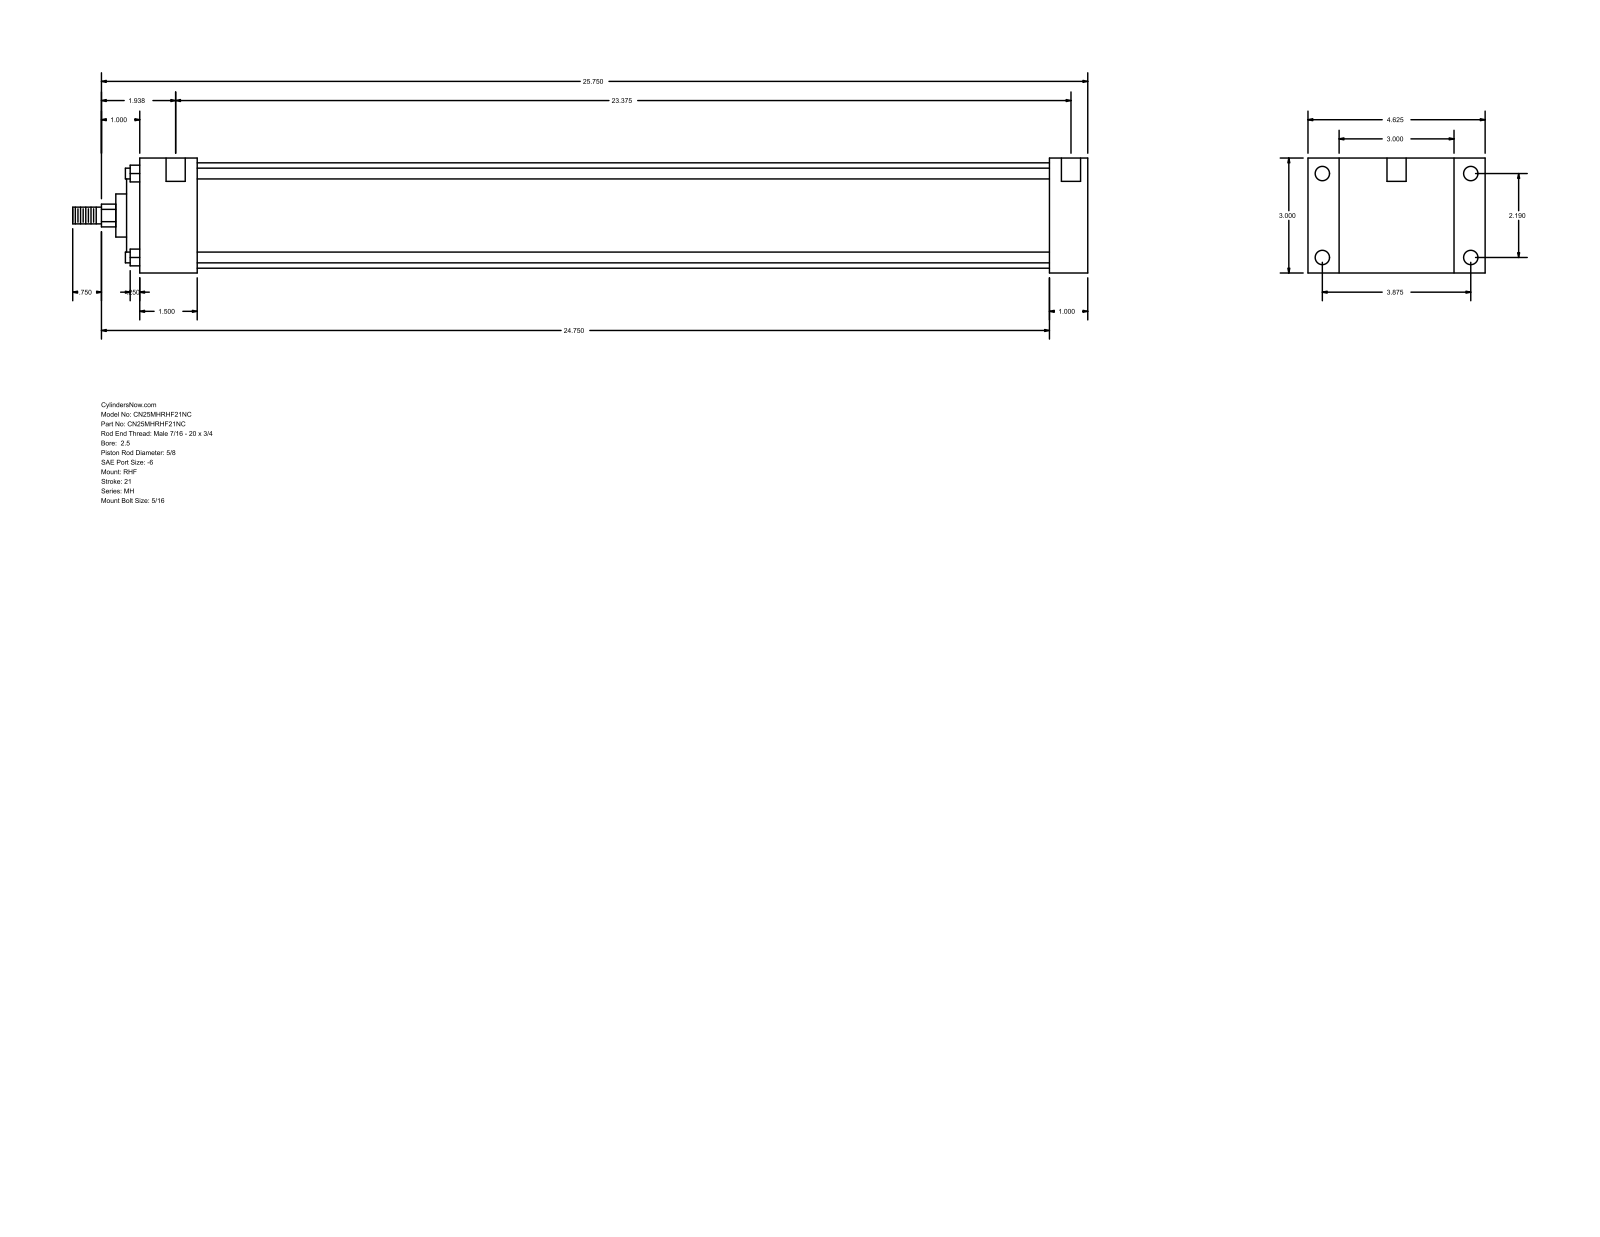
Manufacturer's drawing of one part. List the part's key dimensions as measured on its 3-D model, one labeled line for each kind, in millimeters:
Part name (STEP PRODUCT): MH_RHF__0250_0.625
STEP written by: GSSL Pune (CONFIG_CONTROL_DESIGN)
Units: millimetres
Bodies: 0 solids, 90 faces (61 planar, 29 cylindrical, 0 other)
Overall size (bounding box): 673.1 × 117.47 × 76.2
Round holes (diameter × count): ⌀5.56 ×4, ⌀9.53 ×4, ⌀12.7 ×2
Round bosses / shafts (diameter × count): ⌀7.14 ×4, ⌀69.85 ×1, ⌀55.55 ×1, ⌀28.57 ×1, ⌀15.88 ×1, ⌀11.11 ×1
Partial cylindrical surfaces — rounded edges, fillets, slot ends (radius × count): R7.54 ×1
Main face-to-face distances: 76.2, 25.4, 20.64, 96.84, 628.65, 603.25, 38.1, 117.48, 565.15, 590.55
Hole centre spacings: 55.62, 98.42, 113.05, 601.66, 3.17, 4.76, 593.73, 596.9
